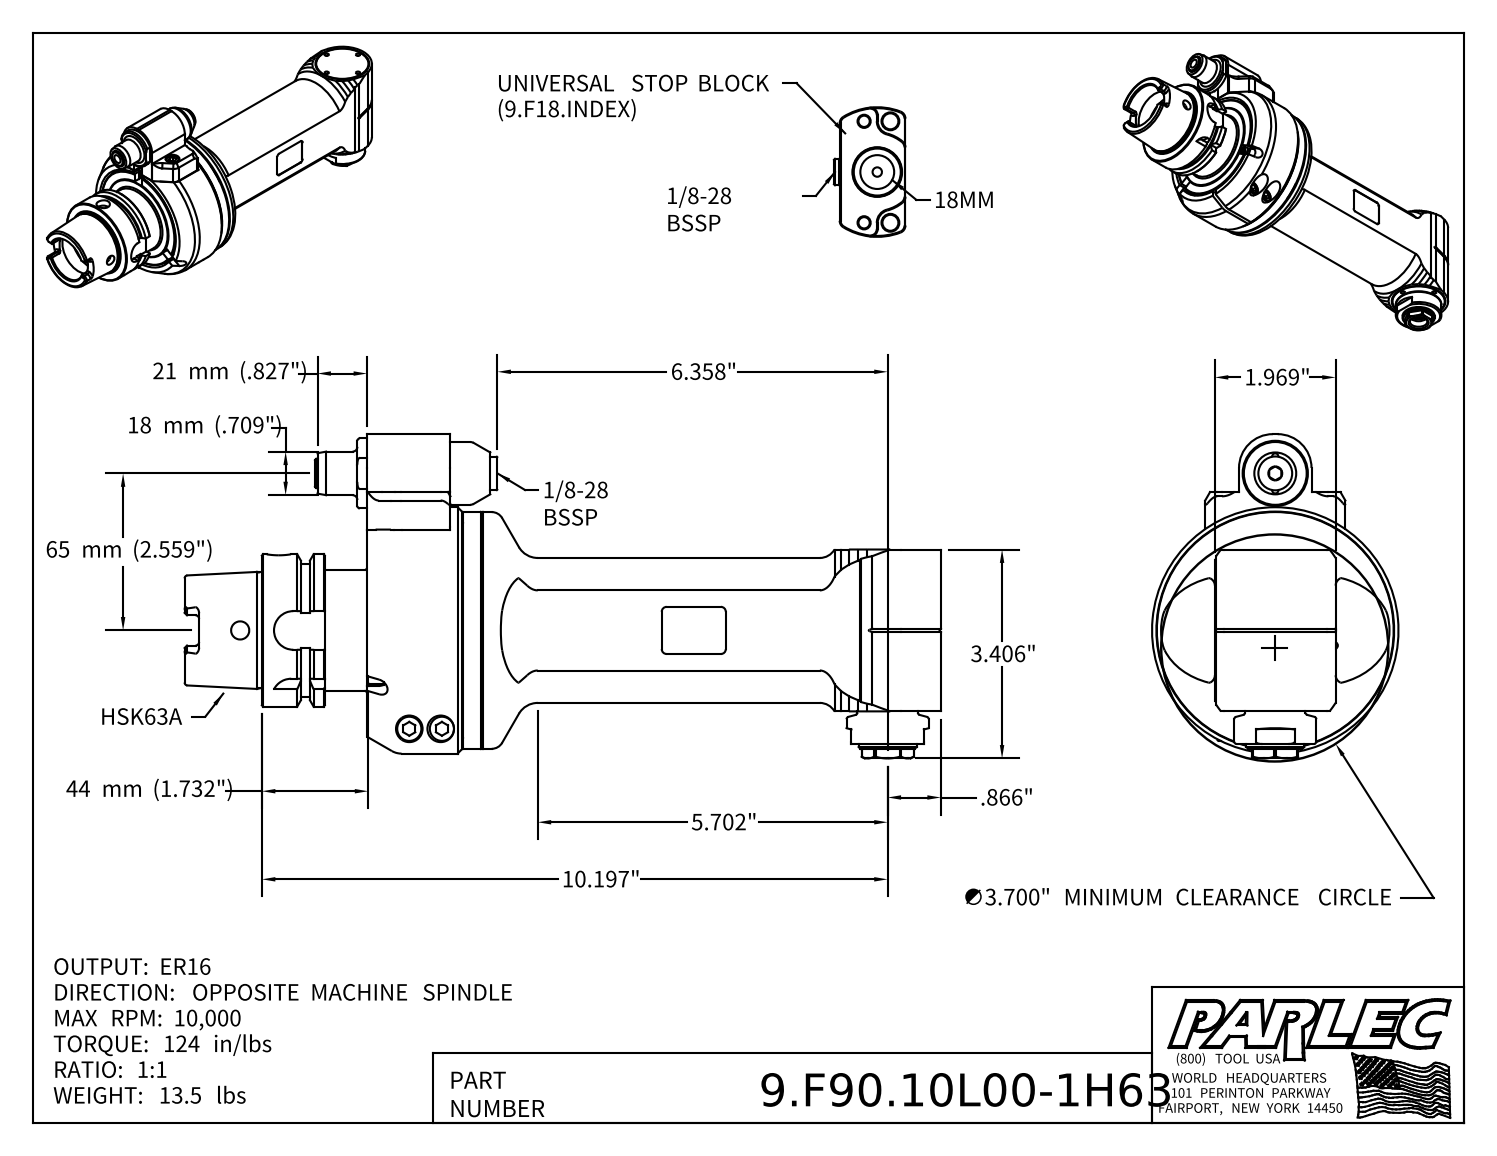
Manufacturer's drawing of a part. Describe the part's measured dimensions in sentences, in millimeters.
The part is named "9.F90.10L00-1H63; 9_GA1_566_2 (EVO, Type 1, H63A, 65mm); 9FL1ATC; 9HSK631ATC (+4 more)". Its 3-D file was written by "Autodesk Inventor 2022 (AUTOMOTIVE_DESIGN)". It is 7 solids with 632 faces: 287 planar, 163 cylindrical and 182 other. Overall it measures 313 by 134.2 by 102 millimeters. Its volume is 1 079 000 cubic millimeters and its surface area 168 100 square millimeters. Round holes: 20 of diameter 8.5, 4 of diameter 3.2, 3 of diameter 11, 2 of diameter 2.6, 2 of diameter 4.2, 2 of diameter 5, 2 of diameter 10.4, 2 of diameter 12.5, 1 of diameter 2.5, 1 of diameter 3, 1 of diameter 6.5, 1 of diameter 7. Round bosses or shafts: 4 of diameter 10, 4 of diameter 6, 2 of diameter 18, 2 of diameter 8, 2 of diameter 2.5, 1 of diameter 102, 1 of diameter 98.4, 1 of diameter 98. Partial cylindrical surfaces (rounded edges, fillets, slot ends): 12 of radius 2, 6 of radius 1.5, 4 of radius 2.9, 4 of radius 4, 4 of radius 8, 2 of radius 0.4, 2 of radius 0.5, 2 of radius 1. The main face-to-face distances are 32, 50, 0.5, 26, 39.5, 7, 7.5, 8.5, 25, 5. The hole center spacings are 38.5, 46.3, 37.3, 54.5, 76.3, 10.7, 61.5, 67.3.
